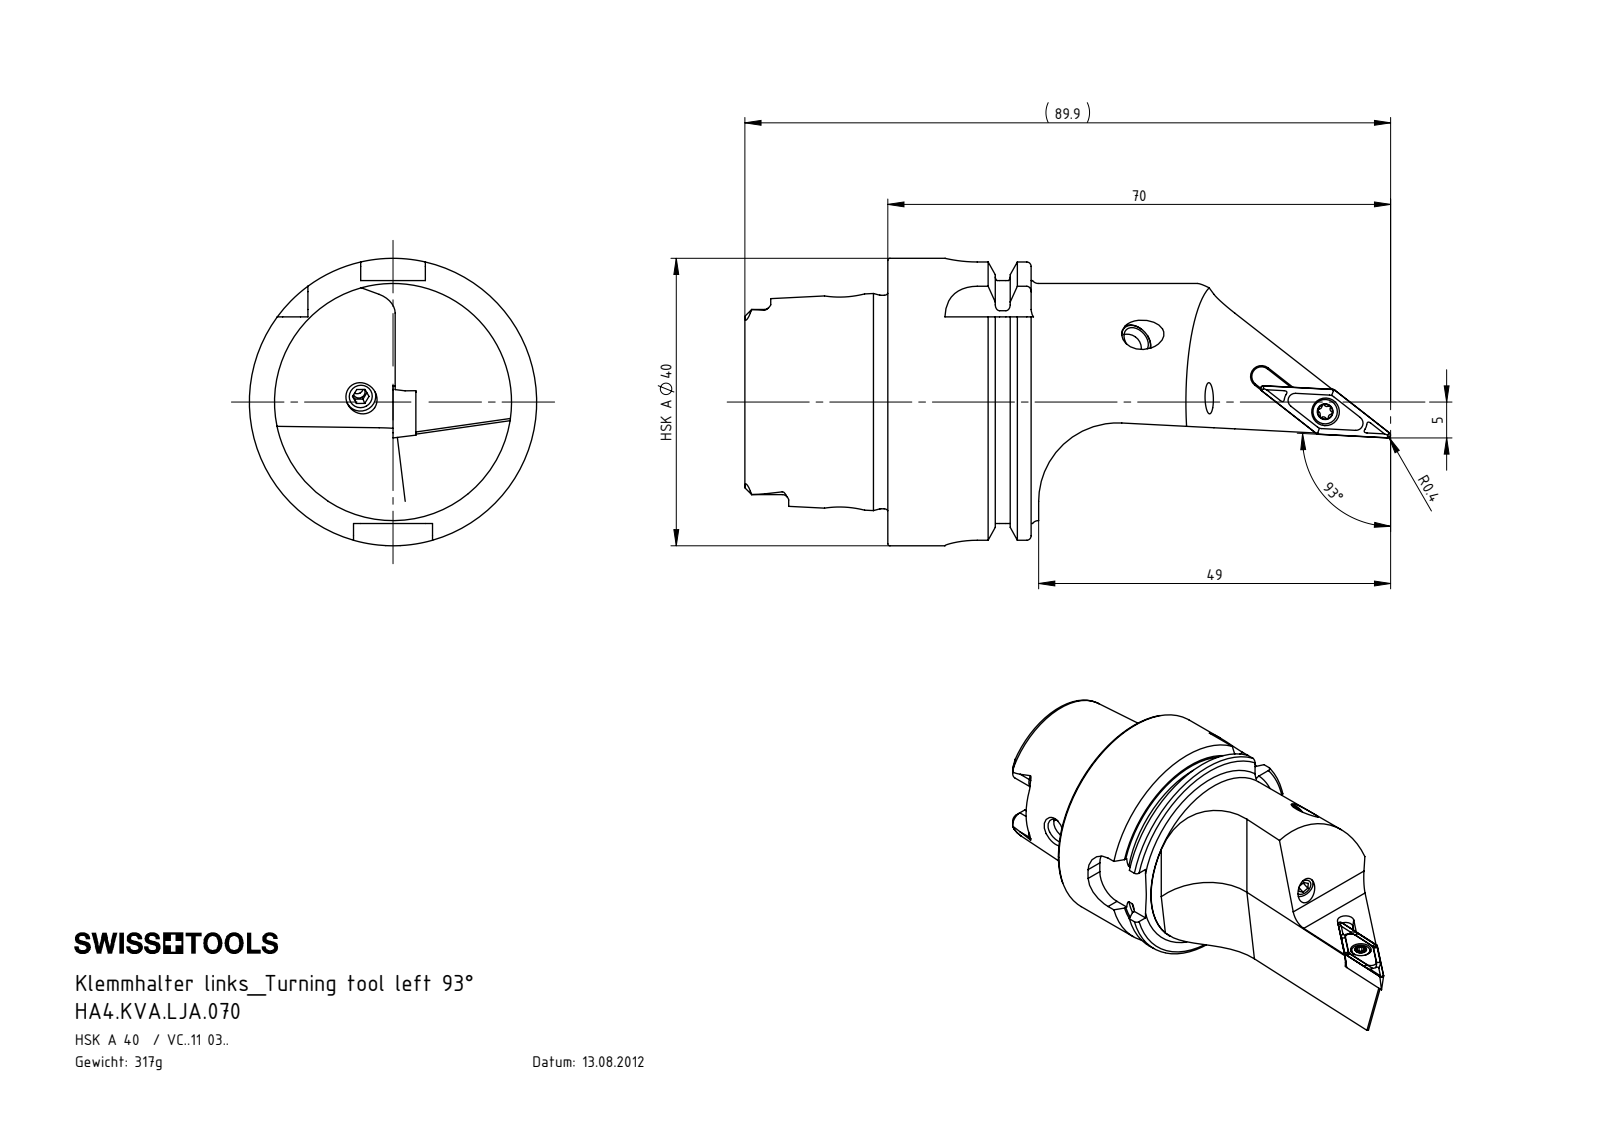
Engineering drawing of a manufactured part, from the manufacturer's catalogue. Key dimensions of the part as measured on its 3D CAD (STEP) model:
Part name (STEP PRODUCT): ISO 4026 - M5 x 8_Sonder mit Bohrung 1.5; KVT_MB_600_050; VCGT110304; WCA-ER2.001.006_A (+2 more)
STEP written by: SolidWorks 2012 (CONFIG_CONTROL_DESIGN)
Units: millimetres
Bodies: 6 solids, 323 faces (90 planar, 91 cylindrical, 142 other)
Overall size (bounding box): 89.88 × 40 × 40
Volume: 40 309 mm³ · Surface area: 13 802 mm²
Round holes (diameter × count): ⌀4 ×2, ⌀4.2 ×2, ⌀1.5 ×1, ⌀2.05 ×1, ⌀2.8 ×1, ⌀3.85 ×1, ⌀4.6 ×1, ⌀5 ×1, ⌀10 ×1, ⌀11 ×1, ⌀12.5 ×1, ⌀21 ×1
Round bosses / shafts (diameter × count): ⌀5 ×2, ⌀40 ×1, ⌀34.75 ×1, ⌀33 ×1, ⌀29.71 ×1, ⌀3.4 ×1, ⌀2.5 ×1
Partial cylindrical surfaces — rounded edges, fillets, slot ends (radius × count): R0.21 ×6, R0.9 ×6, R0.36 ×5, R1.88 ×4, R4.5 ×4, R0.36 ×1, R1.35 ×1, R3 ×1
Main face-to-face distances: 7.95, 19.95, 12, 19.9, 27.85, 39.85, 35.7, 15.8, 7.85, 4.15
Hole centre spacings: 53.9, 53.96
